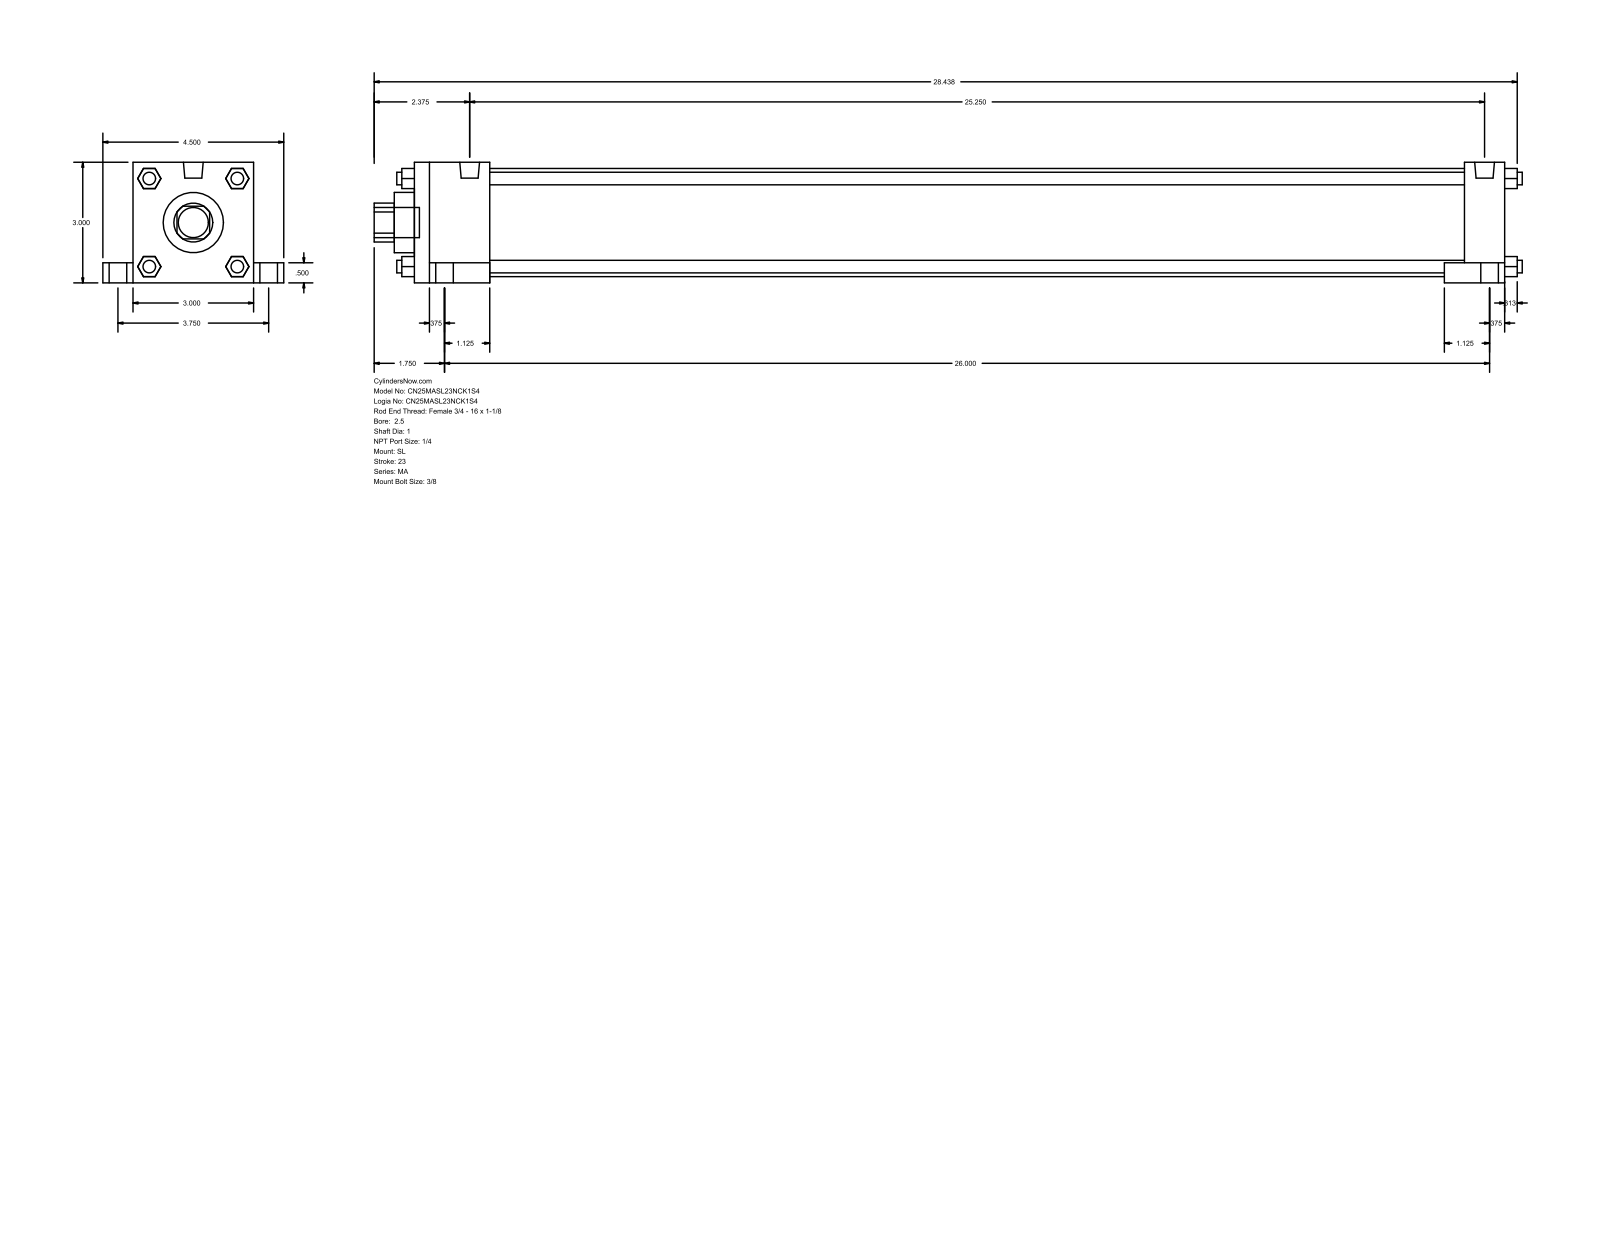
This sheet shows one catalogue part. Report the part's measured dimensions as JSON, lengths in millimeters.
{"part_name": "MA_SL__0250_1", "step_written_by": "GSSL Pune (CONFIG_CONTROL_DESIGN)", "units": "millimeters", "bodies": {"solids": 0, "faces": 148, "planar": 112, "cylindrical": 36, "other": 0}, "overall_size": [725.49, 114.3, 76.2], "round_holes": [[25.4, 1], [38.1, 1], [68.33, 1]], "round_bosses_or_shafts": [[7.94, 8], [17.46, 4], [11.11, 4], [12.49, 2], [19.05, 1]], "partial_cylinders_radius": [[12.29, 1]], "face_to_face_distances": [76.2, 688.98, 12.7, 615.95, 25.4, 47.63, 641.35, 663.58, 19.05, 95.25]}
